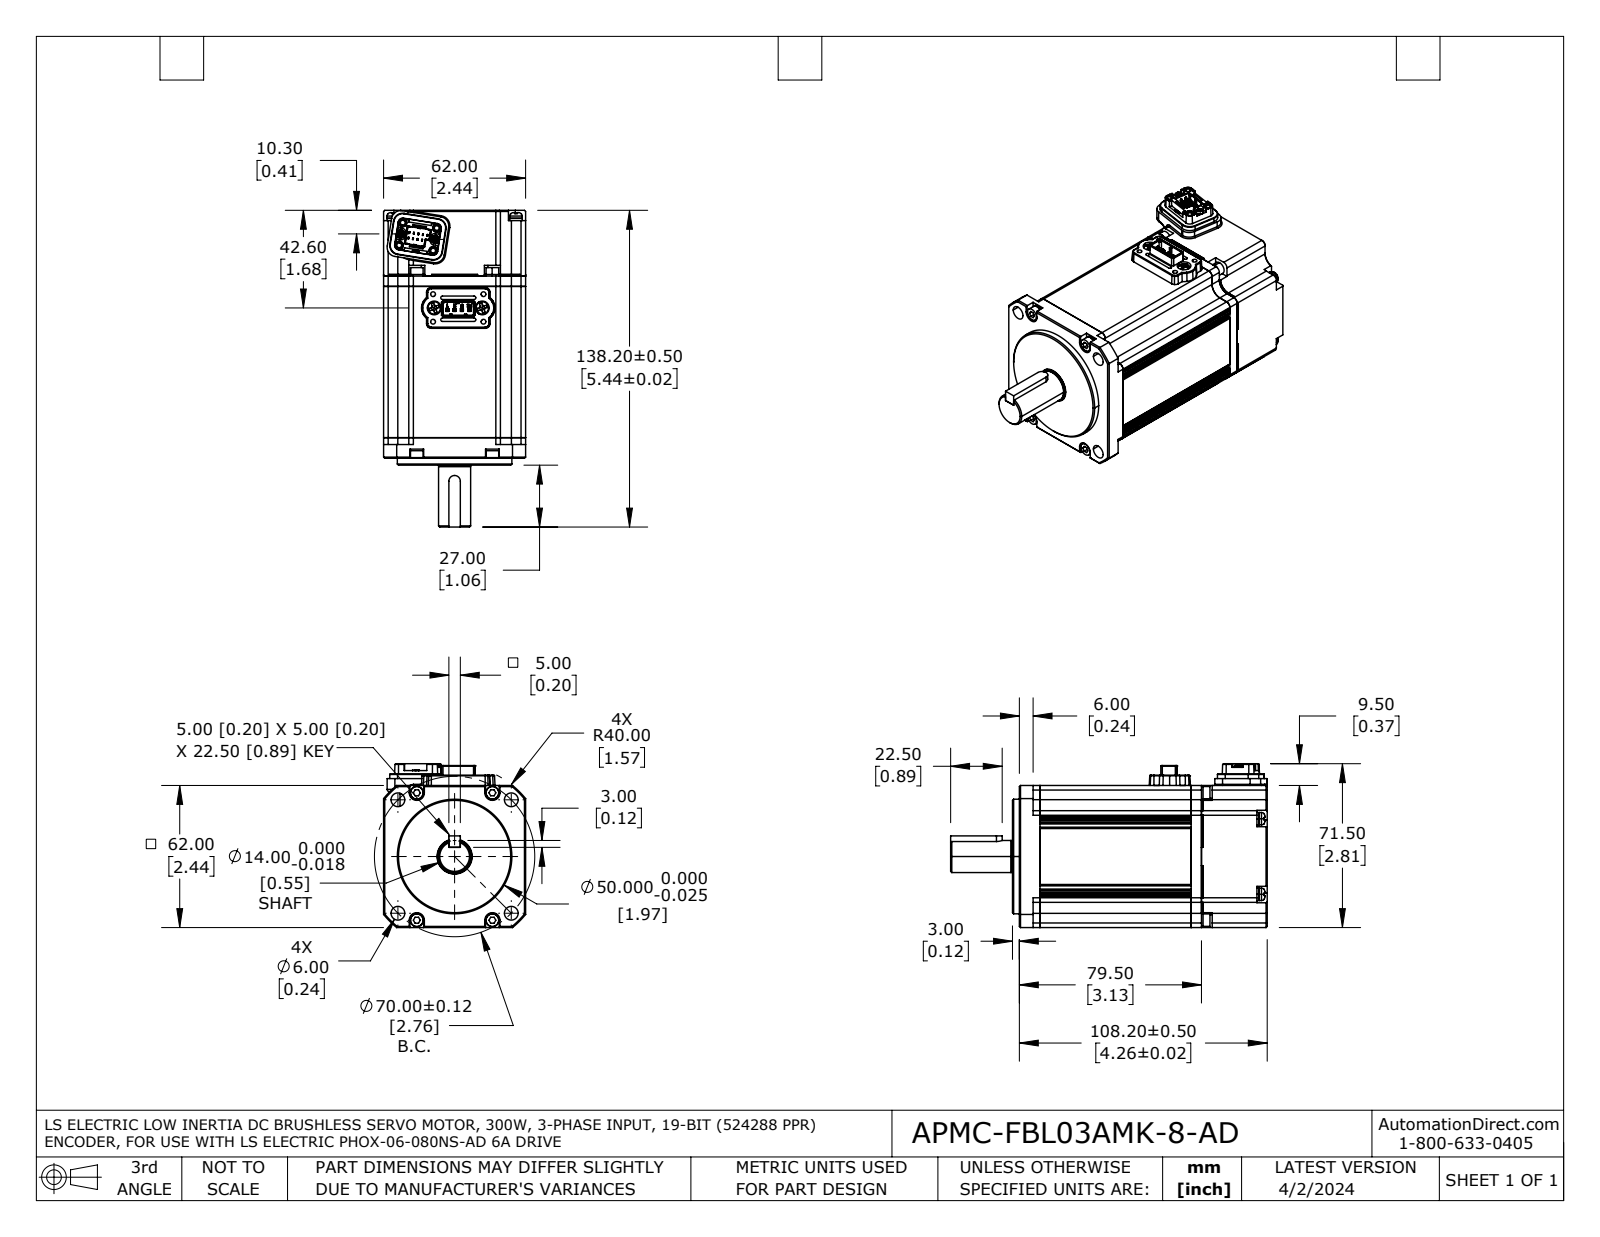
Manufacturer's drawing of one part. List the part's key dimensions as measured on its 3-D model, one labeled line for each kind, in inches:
Part name (STEP PRODUCT): APMC-FBL03AMK-8-AD
STEP written by: SolidWorks 2021 (AUTOMOTIVE_DESIGN)
Units: inches
Bodies: 45 solids, 1909 faces (1167 planar, 543 cylindrical, 199 other)
Overall size (bounding box): 5.441 × 2.815 × 2.441
Volume: 23.19 in³ · Surface area: 117.6 in²
Round holes (diameter × count): ⌀0.083 ×10, ⌀0.138 ×8, ⌀0.118 ×6, ⌀0.236 ×6, ⌀0.122 ×4, ⌀0.079 ×2, ⌀0.13 ×1, ⌀0.134 ×1, ⌀0.602 ×1
Round bosses / shafts (diameter × count): ⌀0.213 ×6, ⌀0.22 ×4, ⌀0.217 ×4, ⌀0.118 ×4, ⌀0.087 ×2, ⌀1.969 ×1, ⌀0.591 ×1, ⌀0.583 ×1
Partial cylindrical surfaces — rounded edges, fillets, slot ends (radius × count): R0.008 ×20, R0.012 ×20, R0.039 ×12, R0.006 ×9, R0.079 ×8, R0.118 ×8, R0.018 ×7, R0.004 ×6
Main face-to-face distances: 2.441, 0.177, 0.028, 2.598, 2.776, 0.205, 2.803, 0.433, 2.008, 0.118
Hole centre spacings: 1.762, 0.237, 0.335, 0.346, 0.602, 0.63, 0.879, 1.239
